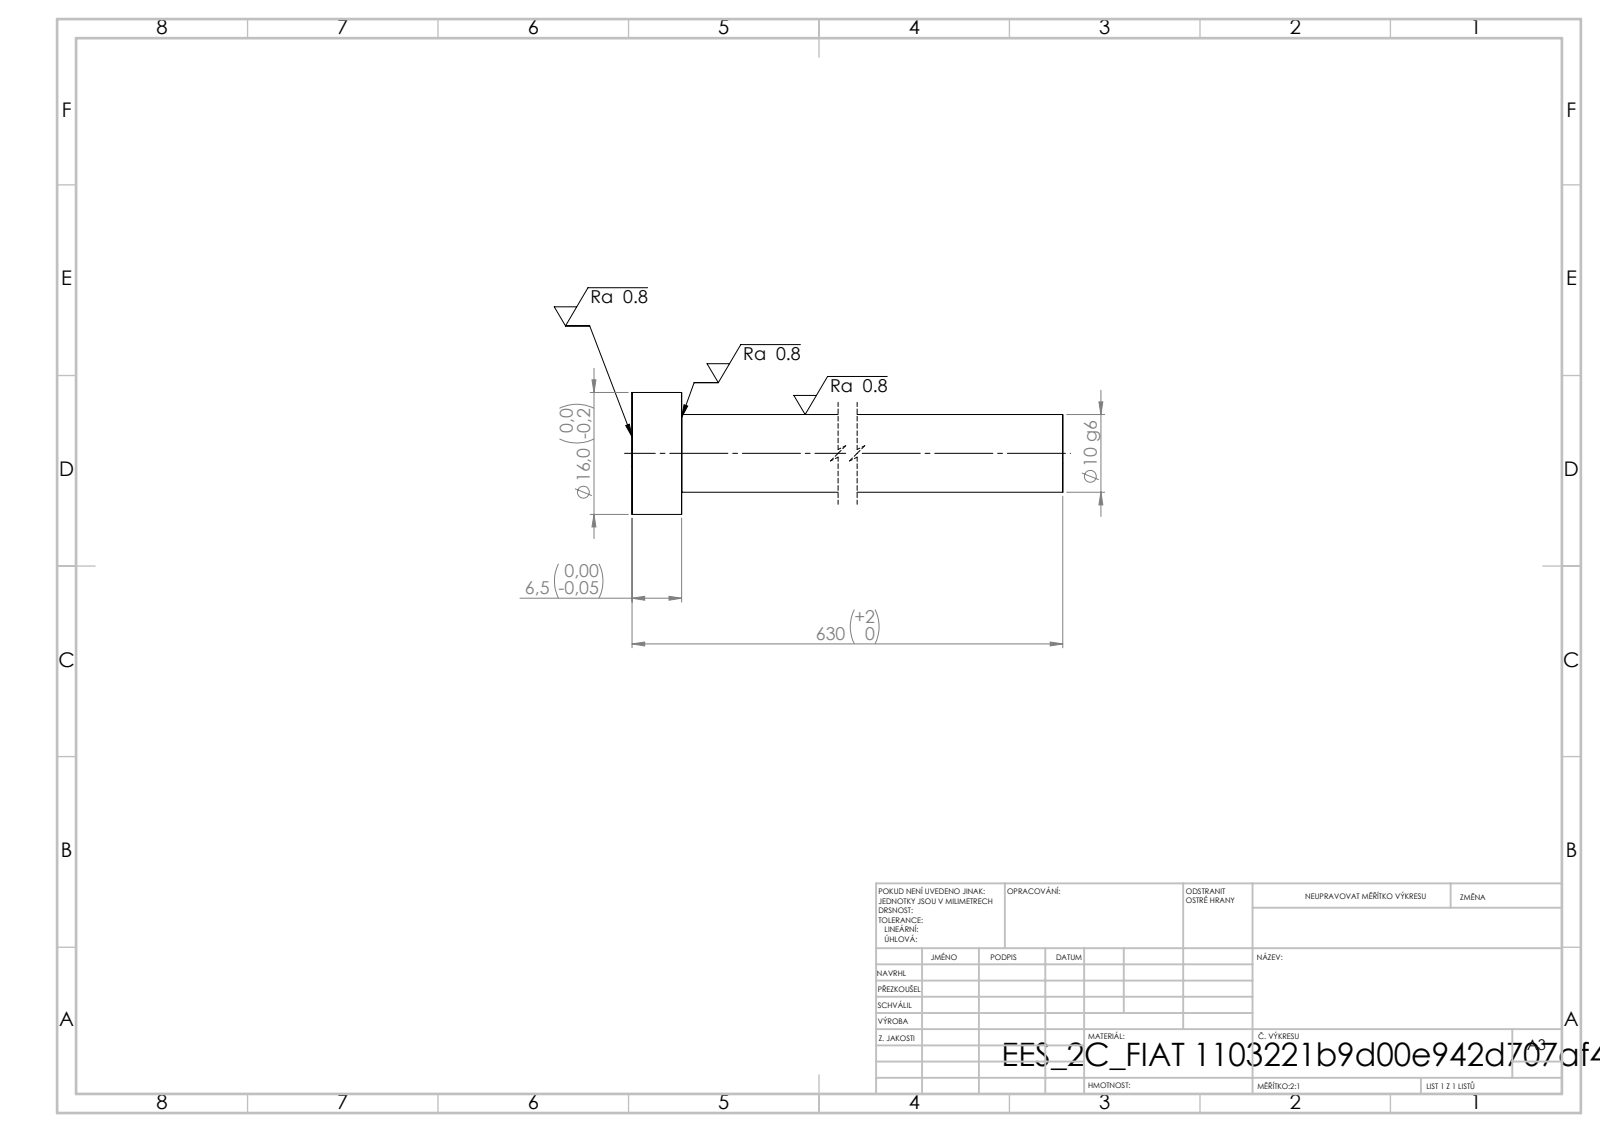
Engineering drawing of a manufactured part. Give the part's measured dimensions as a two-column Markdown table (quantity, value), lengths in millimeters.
| quantity | value |
| --- | --- |
| STEP written by | SolidWorks 2019 (CONFIG_CONTROL_DESIGN) |
| units | millimeters |
| bodies | 1 solid, 7 faces (3 planar, 4 cylindrical, 0 other) |
| overall size | 630 × 16 × 16 |
| volume | 52 255 mm³ |
| surface area | 20 708 mm² |
| round bosses / shafts (diameter × count) | 16 × 1, 10.2 × 1 |
| main face-to-face distances | 6.5, 630, 623.5 |
